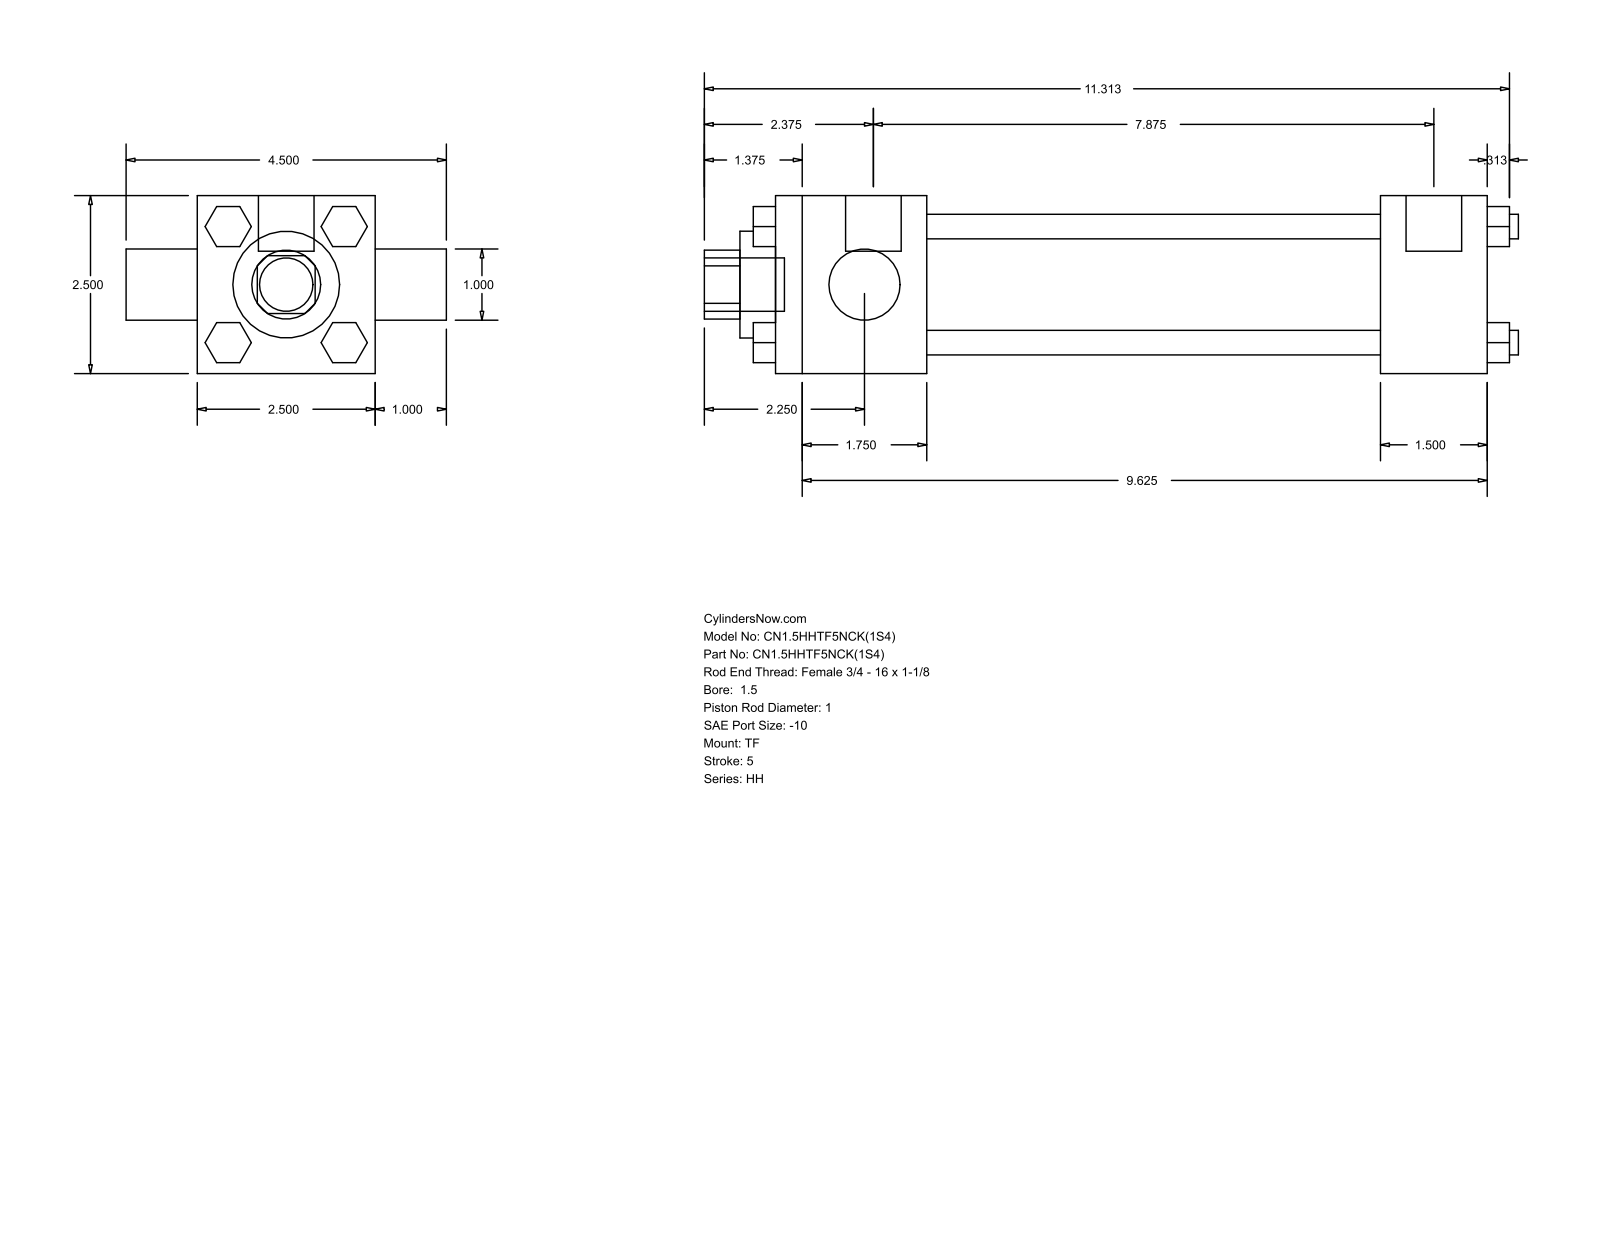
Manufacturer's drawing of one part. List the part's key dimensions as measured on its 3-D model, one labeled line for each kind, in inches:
Part name (STEP PRODUCT): HH_TF__0150_1
STEP written by: GSSL Pune (CONFIG_CONTROL_DESIGN)
Units: inches
Bodies: 0 solids, 120 faces (92 planar, 28 cylindrical, 0 other)
Overall size (bounding box): 11.437 × 4.5 × 2.5
Round holes (diameter × count): ⌀1 ×2, ⌀1.5 ×1, ⌀1.75 ×1
Round bosses / shafts (diameter × count): ⌀0.345 ×4, ⌀0.219 ×3, ⌀0.781 ×2, ⌀0.75 ×1
Partial cylindrical surfaces — rounded edges, fillets, slot ends (radius × count): R0.484 ×1
Main face-to-face distances: 2.5, 7.875, 6.375, 1.5, 2.125, 8.5, 10, 10.313, 1, 0.815
